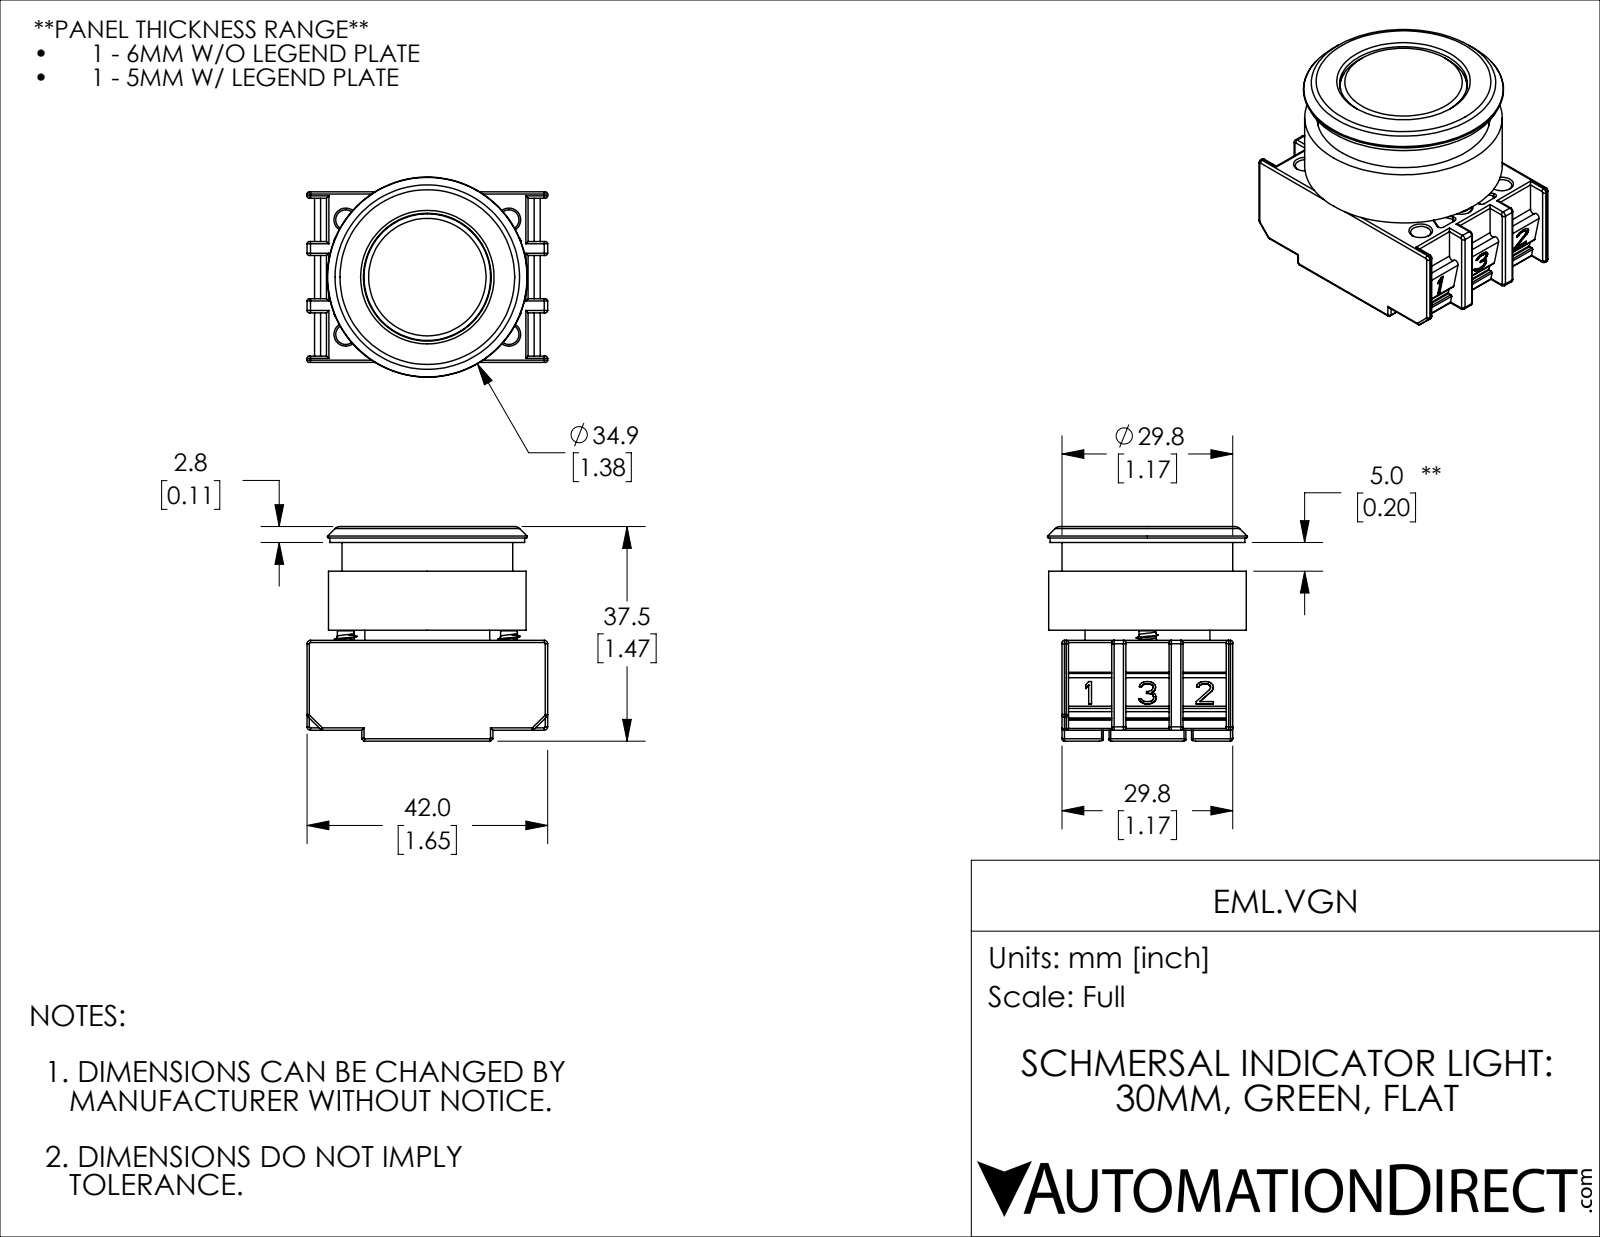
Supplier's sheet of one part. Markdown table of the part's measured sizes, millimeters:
| quantity | value |
| --- | --- |
| part name | EML.VGN |
| STEP written by | SolidWorks 2019 (CONFIG_CONTROL_DESIGN) |
| units | millimeters |
| bodies | 3 solids, 1372 faces (495 planar, 474 cylindrical, 403 other) |
| overall size | 42 × 37.45 × 34.93 |
| volume | 22 251 mm³ |
| surface area | 21 607 mm² |
| round holes (diameter × count) | 3.5 × 6, 5.15 × 6, 11 × 1, 12.6 × 1, 15 × 1, 18 × 1, 22.3 × 1, 24.2 × 1, 26 × 1, 27 × 1, 30.2 × 1 |
| round bosses / shafts (diameter × count) | 4.8 × 2, 2.93 × 2, 34.5 × 1, 34 × 1, 29.8 × 1, 25.5 × 1, 24 × 1, 23.8 × 1 |
| partial cylindrical surfaces (radius × count) | 0.4 × 115, 0.3 × 48, 0.2 × 28, 0.6 × 8, 0.5 × 6, 0.1 × 2, 0.6 × 2, 0.8 × 2 |
| main face-to-face distances | 29.8, 14.7, 1.75, 16.45, 3.4, 10, 1.9, 19.35, 19.65, 17.9 |
| hole center spacings | 10, 17.41, 30.2, 28.5, 14.25, 20, 34.82 |
